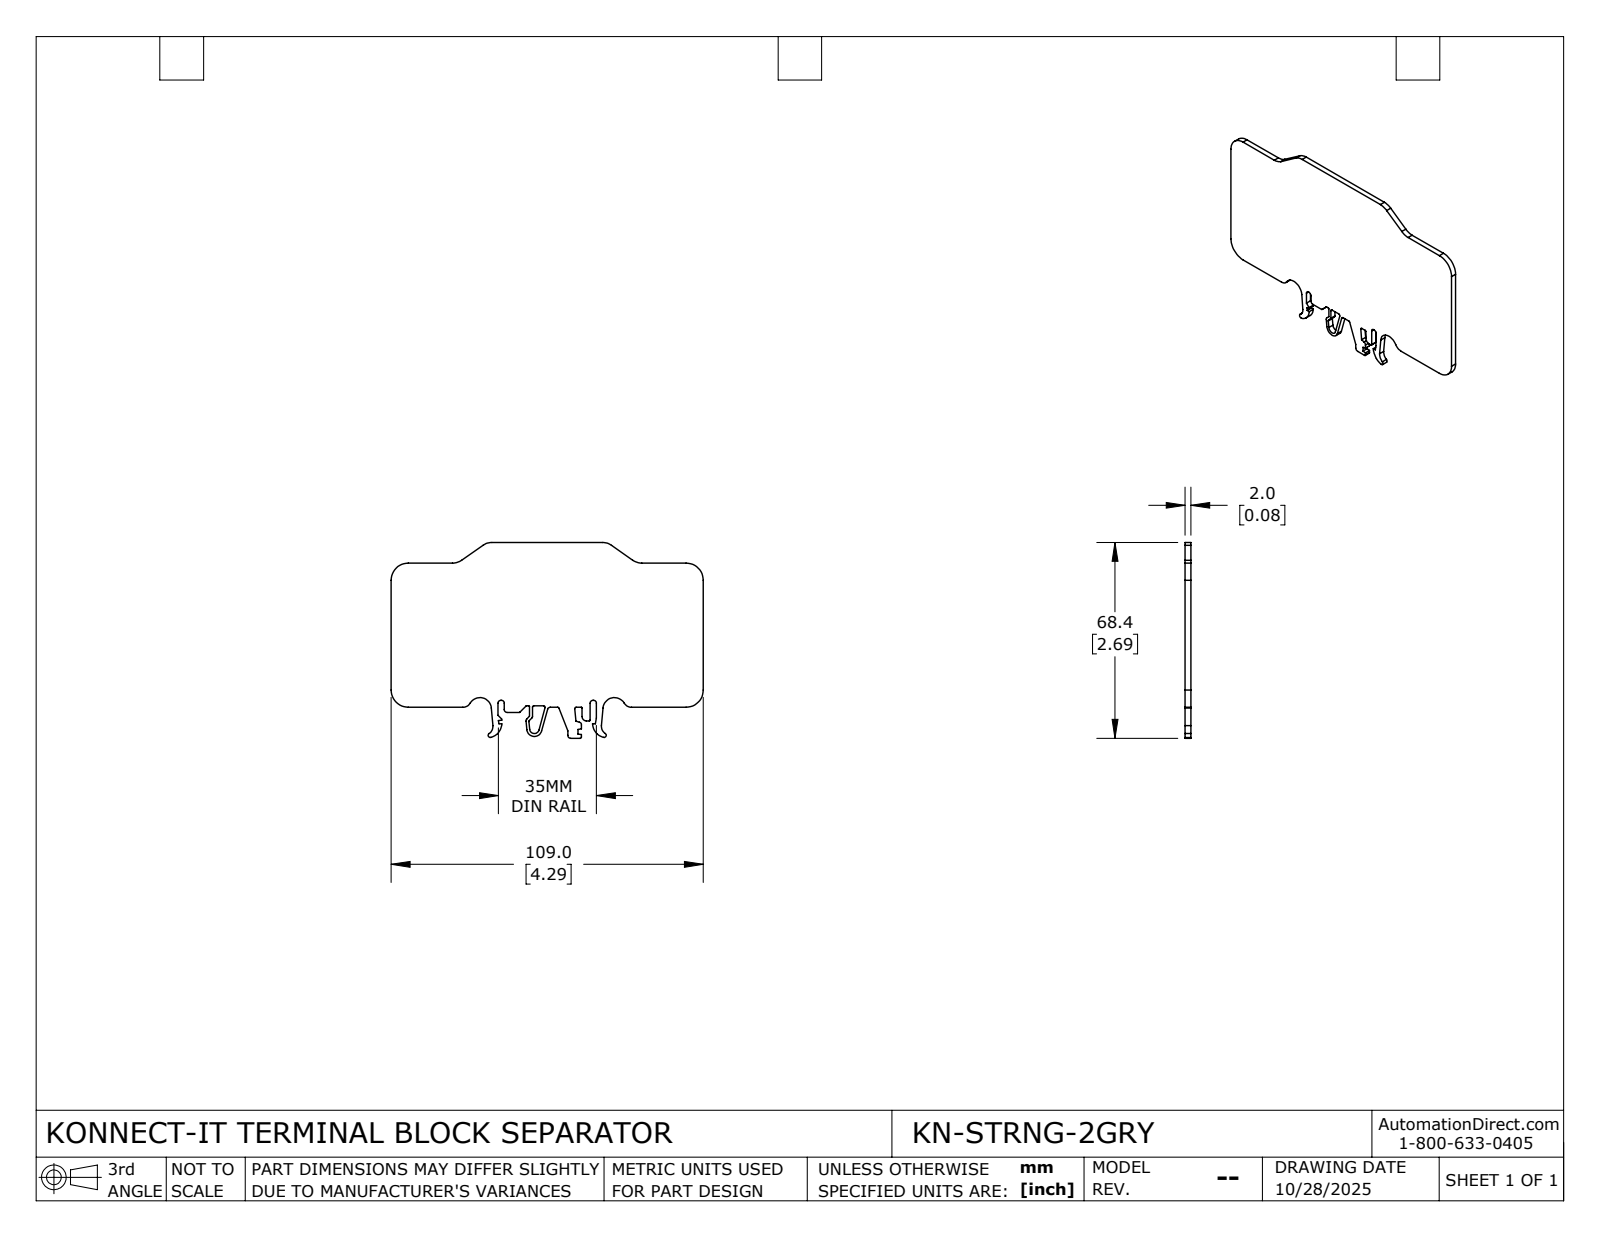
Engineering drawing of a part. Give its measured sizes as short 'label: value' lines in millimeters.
name: KN-STRNG-2GRY
written by: SolidWorks 2024 (CONFIG_CONTROL_DESIGN)
unit: mm
bodies: 1 solid, 99 faces (52 planar, 47 cylindrical, 0 other)
size: 109 × 68.37 × 2
volume: 11 856 mm³; area: 12 760 mm²
rounds: 7× R1, 5× R0.3, 5× R0.5, 4× R3, 4× R5.5, 4× R6, 2× R0.75, 2× R1
face distances: 2, 57.53, 109, 50.32, 7.21, 1, 39.5, 69.5, 71.68, 2.18
